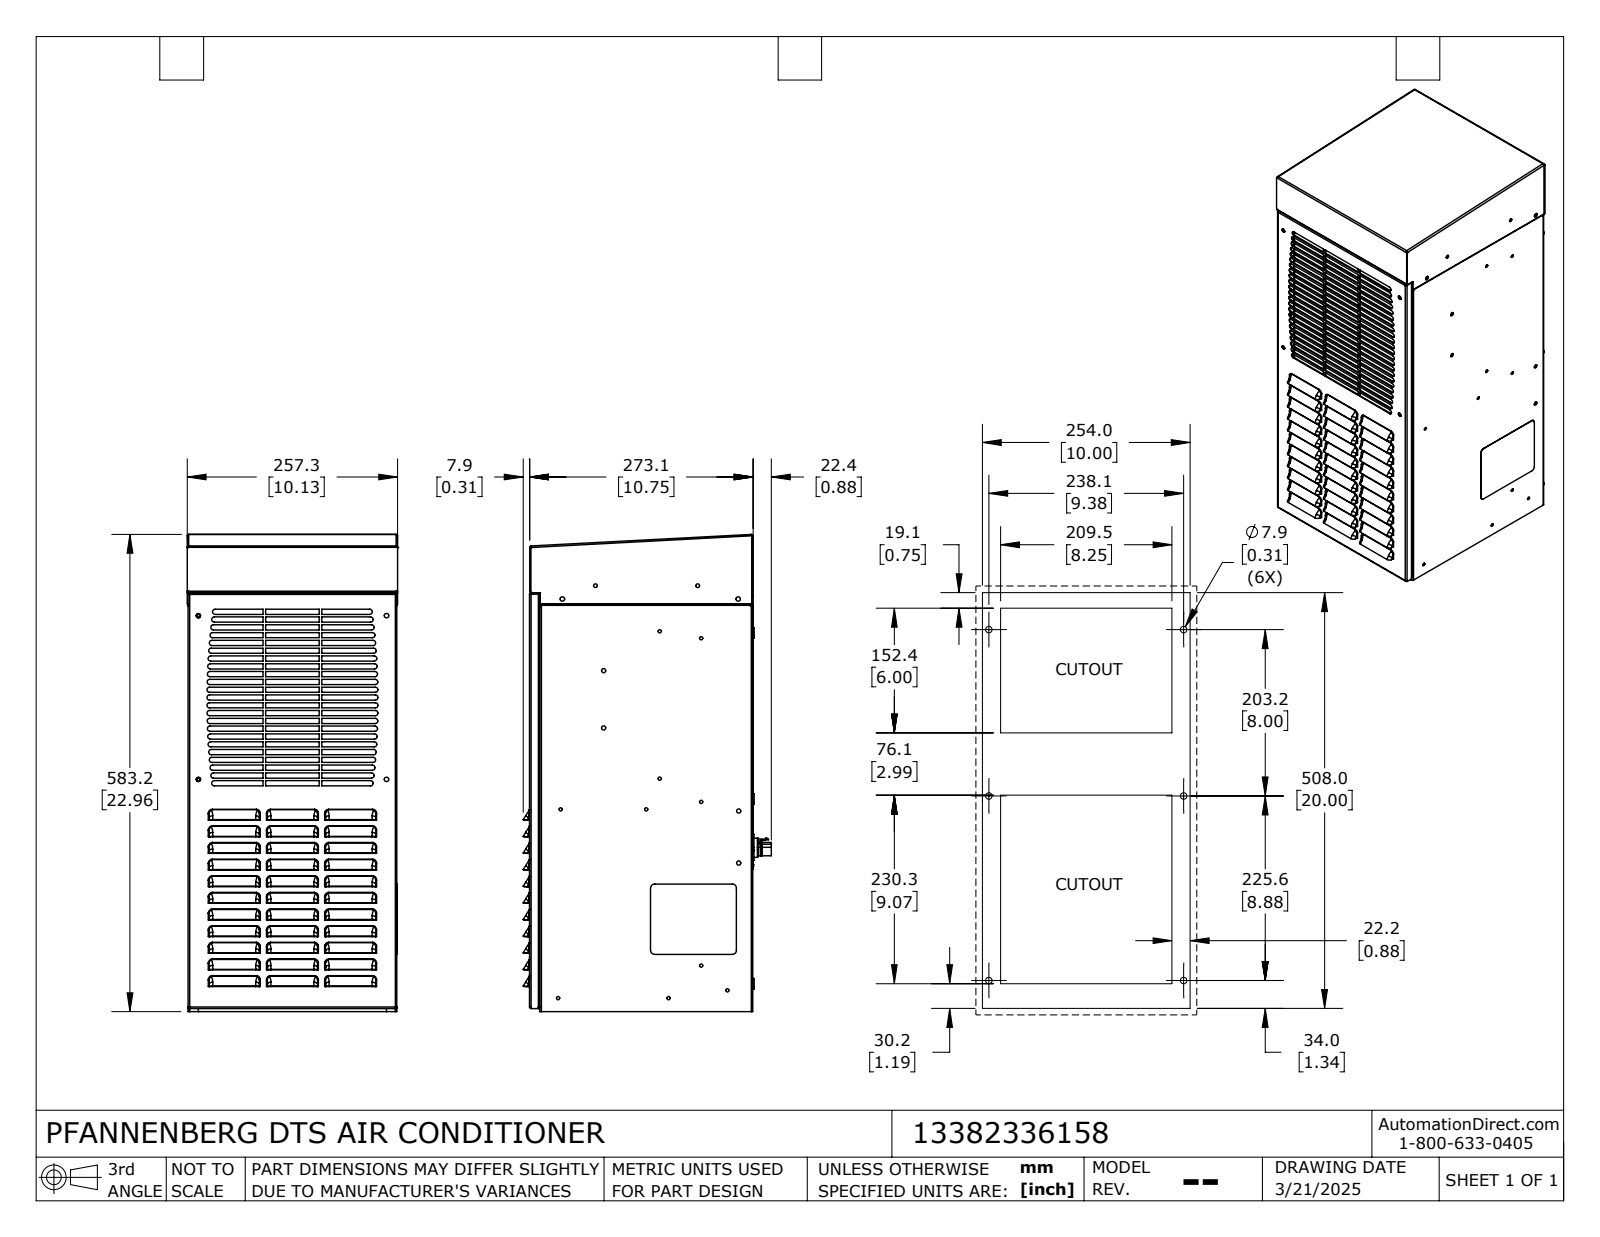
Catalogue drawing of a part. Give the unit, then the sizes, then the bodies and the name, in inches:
Units: inches
Overall size (bounding box): 22.962 × 11.943 × 10.129
Round holes (diameter × count): ⌀0.217 ×12, ⌀0.156 ×10, ⌀0.187 ×8, ⌀0.213 ×8, ⌀0.283 ×6, ⌀0.169 ×5, ⌀0.209 ×5, ⌀0.149 ×4, ⌀0.281 ×4, ⌀0.139 ×2, ⌀0.177 ×2, ⌀0.188 ×2
Round bosses / shafts (diameter × count): ⌀0.512 ×6, ⌀0.079 ×4, ⌀0.28 ×2, ⌀0.273 ×2, ⌀0.259 ×2, ⌀0.984 ×1
Partial cylindrical surfaces — rounded edges, fillets, slot ends (radius × count): R0.125 ×252, R0.17 ×66, R0.031 ×23, R0.076 ×22, R0.045 ×17, R0.09 ×17, R0.031 ×10, R0.076 ×10
Main face-to-face distances: 0.045, 10.711, 10.05, 0.031, 10.095, 10.756, 10.667, 0.572, 10.622, 0.528
Hole centre spacings: 4.921, 0.294, 7.874, 9.195, 0.022, 0.244, 2.5, 7.767
Volume: 2 319 in³ · Surface area: 2 371 in²
Bodies: 1 solid, 3074 faces (1529 planar, 1003 cylindrical, 542 other)
Part name (STEP PRODUCT): 13382336158_Default
STEP written by: SolidWorks 2024 (CONFIG_CONTROL_DESIGN)
